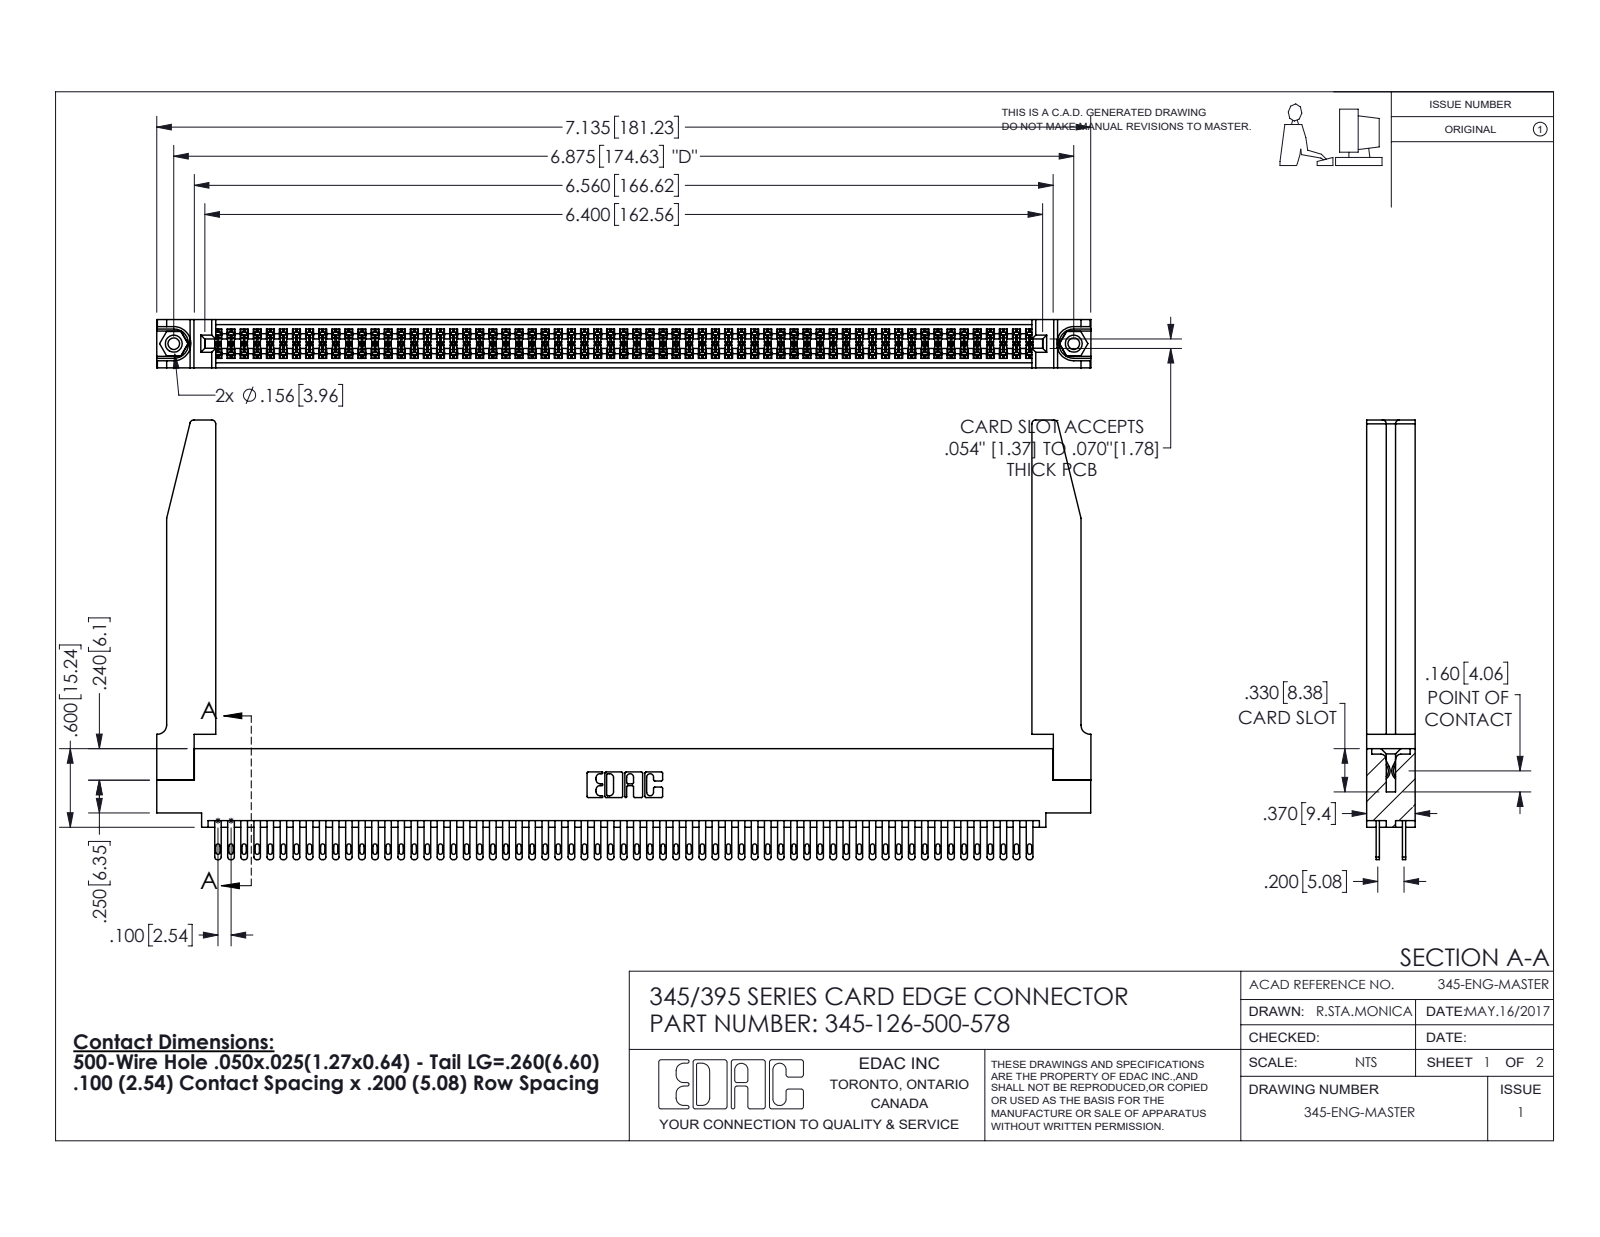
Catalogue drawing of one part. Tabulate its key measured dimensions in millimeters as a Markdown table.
| quantity | value |
| --- | --- |
| part name | 345-220-078_345-220-078; 345-250-001_345-250-001-102; 345-126-500-578; 345 Part_0.110 Offset - 0.156 Dia-TH (+1 more) |
| STEP written by | SolidWorks 2016 (CONFIG_CONTROL_DESIGN) |
| units | millimeters |
| bodies | 131 solids, 6160 faces (3628 planar, 2480 cylindrical, 52 other) |
| overall size | 181.3 × 85.3 × 9.4 |
| volume | 25 890 mm³ |
| surface area | 35 400 mm² |
| round holes (diameter × count) | 2.3 × 2, 3.2 × 2, 4 × 2, 1.6 × 1 |
| round bosses / shafts (diameter × count) | 3.9 × 2 |
| partial cylindrical surfaces (radius × count) | 0.2 × 189, 0.4 × 126, 0.5 × 126, 0.3 × 22, 0.8 × 8, 0.2 × 6, 0.8 × 6, 0.7 × 3 |
| main face-to-face distances | 1.8, 7.6, 9.4, 5.1, 2.5, 6.9, 0.6, 5.7, 4.4, 3.8 |
| hole center spacings | 6.9, 168.6, 174.6 |
